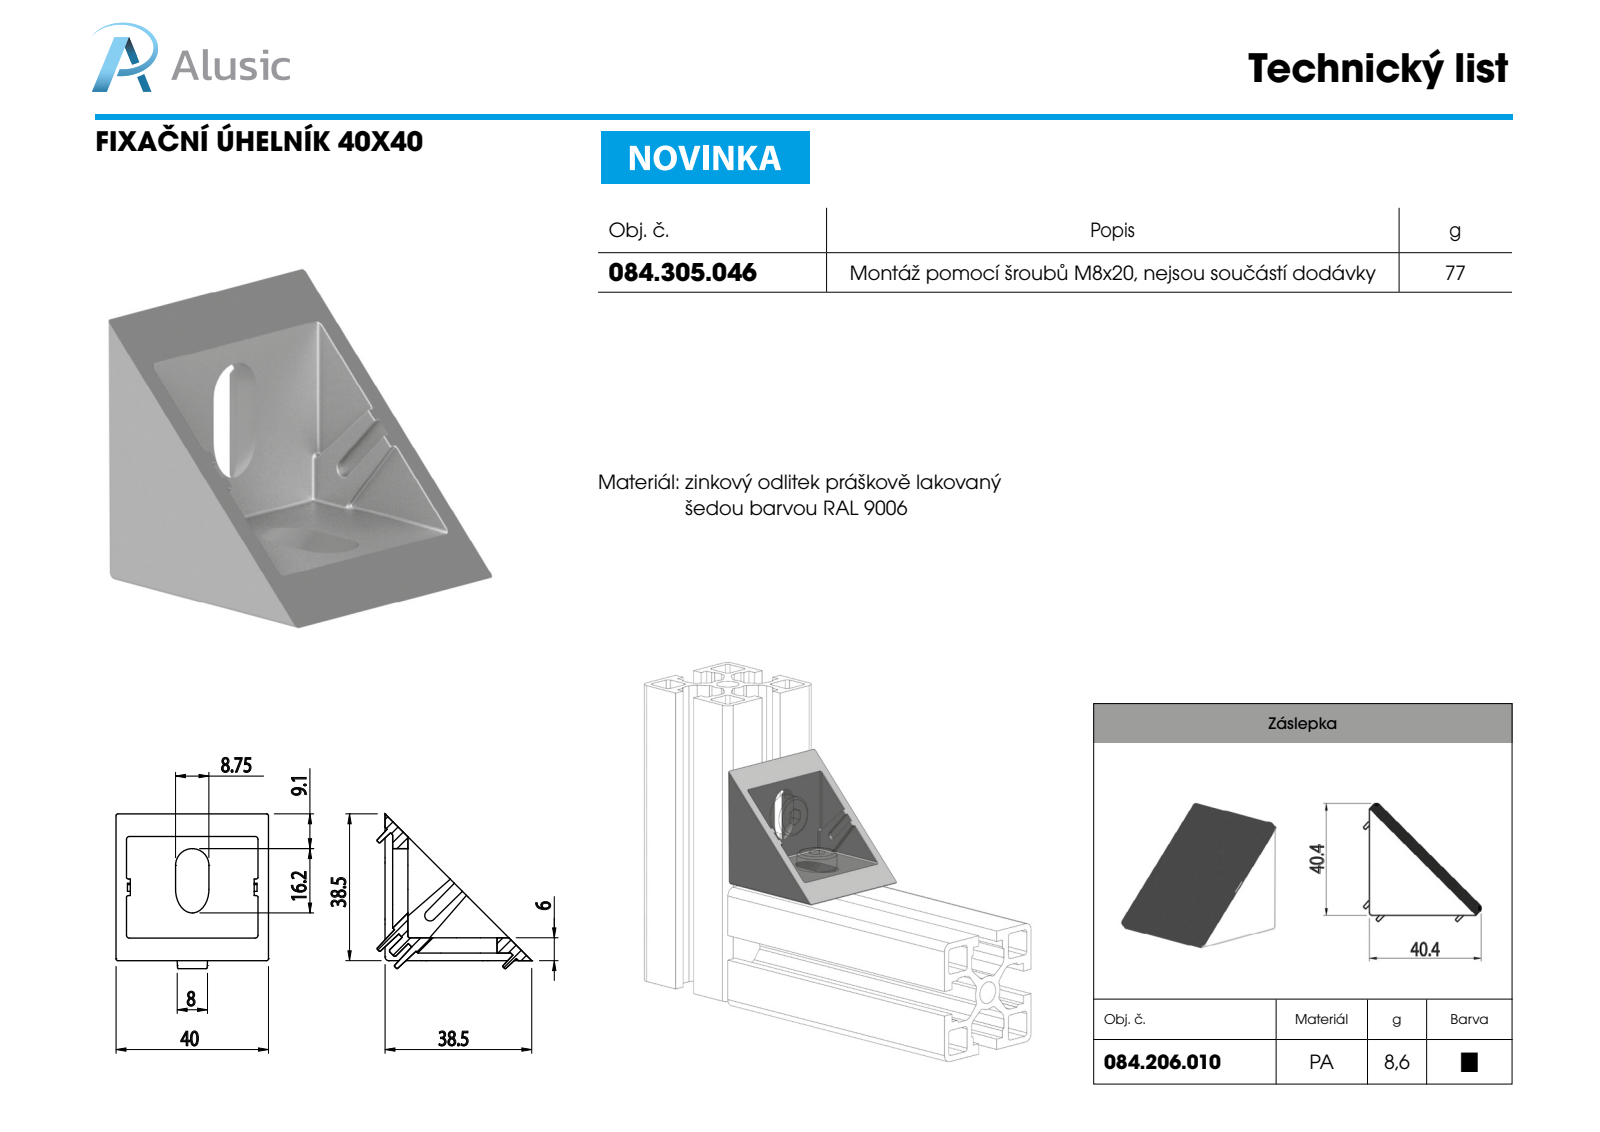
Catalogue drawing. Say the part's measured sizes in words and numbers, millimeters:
The part is named "084.305.046". Its 3-D file was written by "SolidWorks 2018 (CONFIG_CONTROL_DESIGN)". It is 1 solid with 584 faces: 111 planar, 252 cylindrical and 221 other. Overall it measures 40.59 by 40.59 by 40 millimeters. Its volume is 12 293 cubic millimeters and its surface area 9 241 square millimeters. Partial cylindrical surfaces (rounded edges, fillets, slot ends): 76 of radius 0.3, 52 of radius 0.5, 44 of radius 0.25, 17 of radius 1, 4 of radius 4.38, 1 of radius 1.16. The main face-to-face distances are 3, 6, 1, 2, 34, 33, 4, 2.48, 12.62, 21.38.
